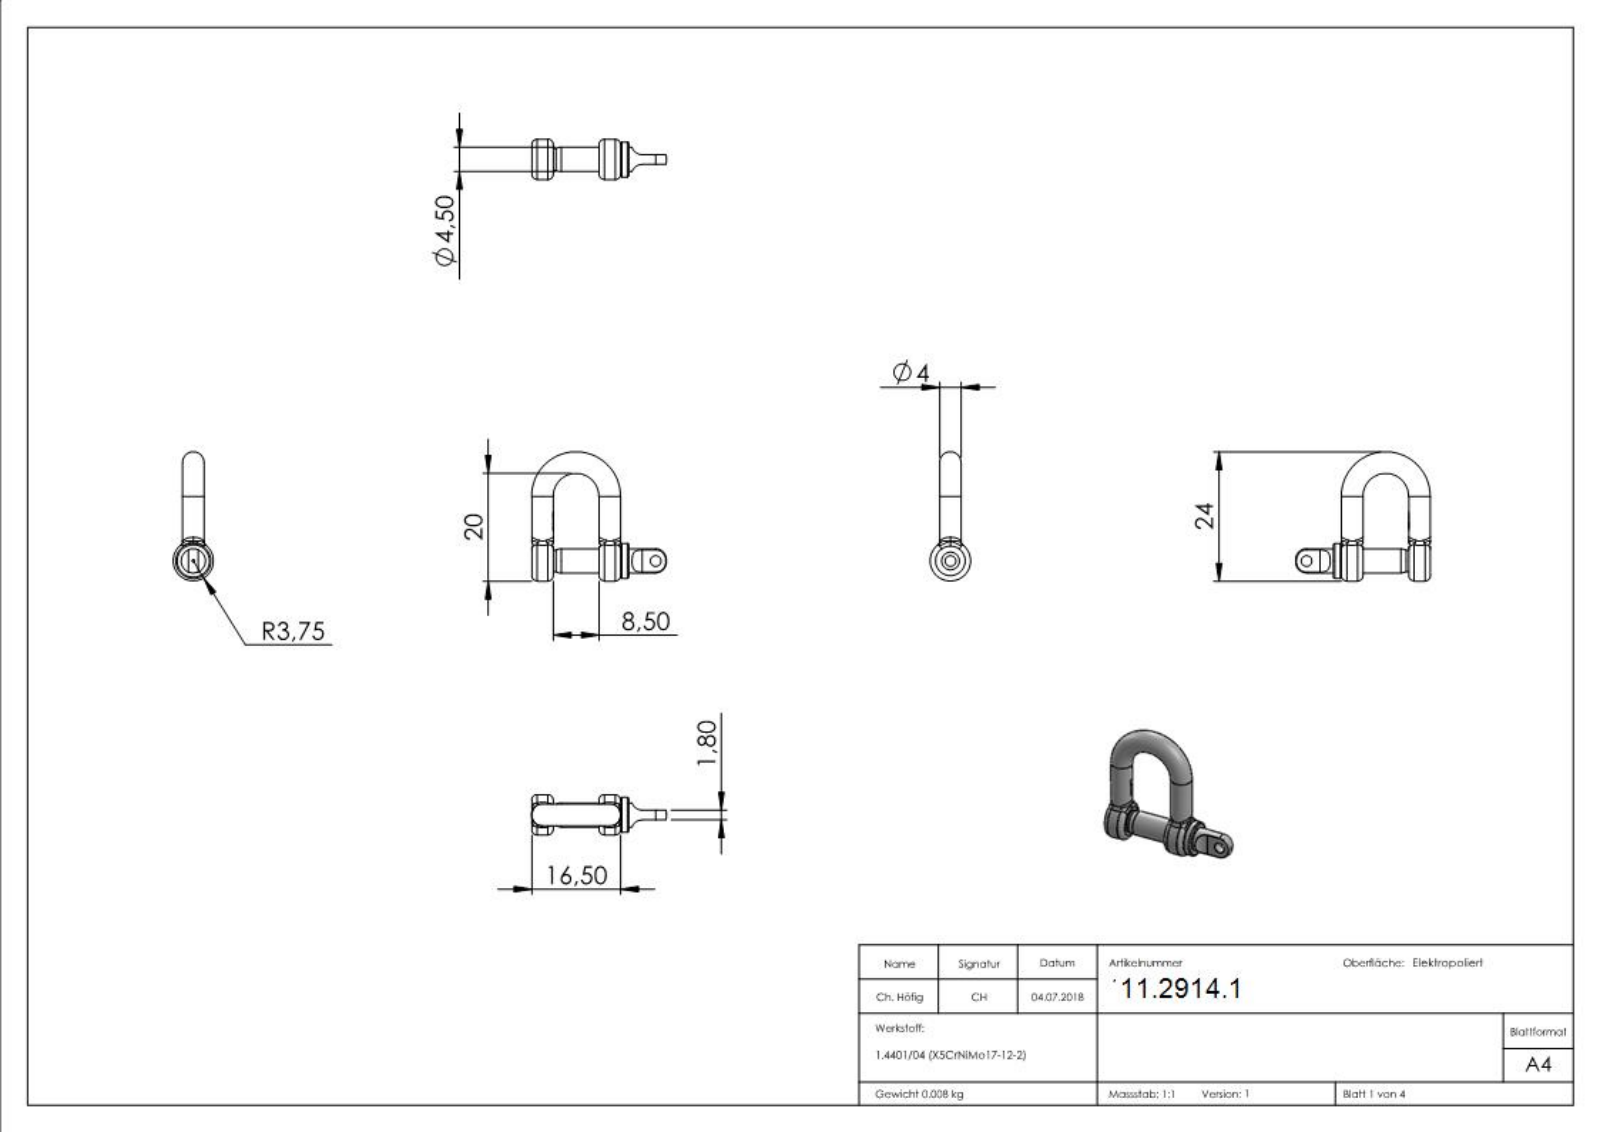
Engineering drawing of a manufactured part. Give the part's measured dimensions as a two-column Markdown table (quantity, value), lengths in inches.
| quantity | value |
| --- | --- |
| part name | 1000500X Teil1_10005004 Teil1; 10005004; 1000500X Teil2_10005004 Teil2 |
| STEP written by | SolidWorks 2015 (CONFIG_CONTROL_DESIGN) |
| units | inches |
| bodies | 2 solids, 288 faces (83 planar, 48 cylindrical, 157 other) |
| overall size | 0.984 × 0.945 × 0.295 |
| volume | 0.063 in³ |
| surface area | 1.838 in² |
| round holes (diameter × count) | 0.079 × 1, 0.13 × 1 |
| round bosses / shafts (diameter × count) | 0.157 × 3, 0.295 × 1, 0.256 × 1, 0.177 × 1 |
| partial cylindrical surfaces (radius × count) | 0.079 × 2, 0.078 × 1 |
| main face-to-face distances | 0.492, 0.157, 0.65, 0.071, 0.059, 0.709, 0.551, 0.335, 0.217, 0.02 |
